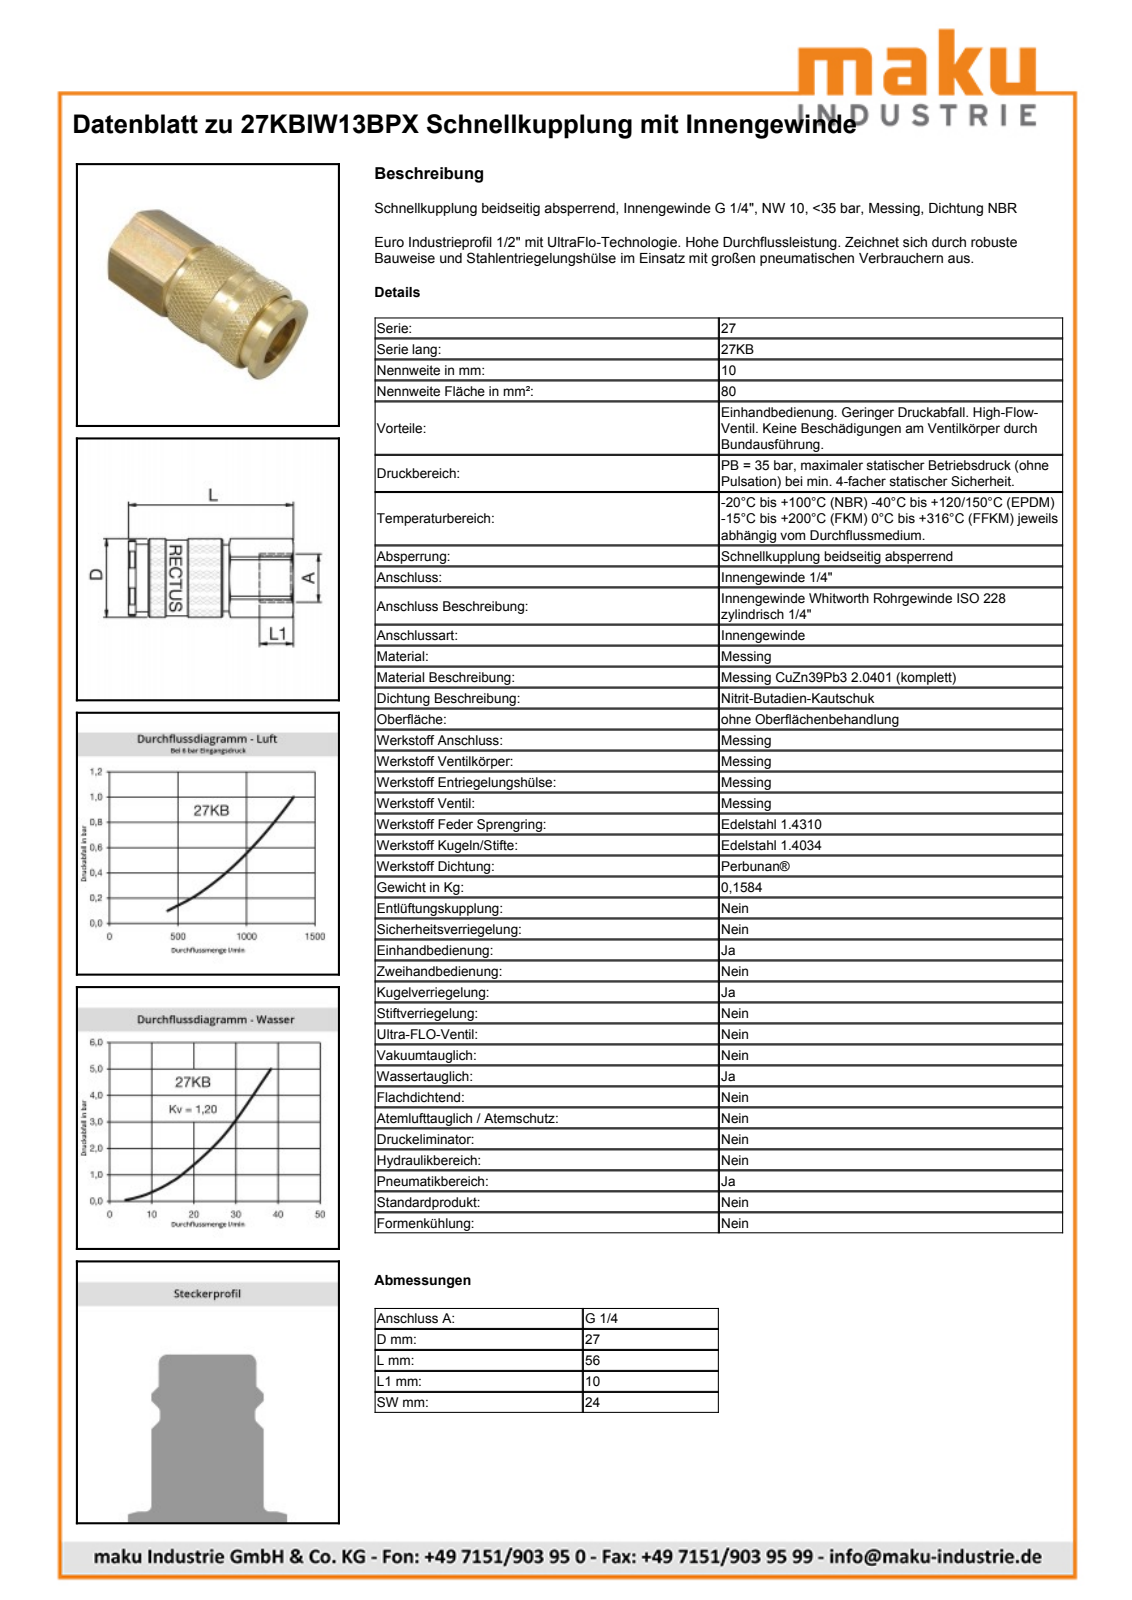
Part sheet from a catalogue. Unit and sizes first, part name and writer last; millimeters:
Units: millimetres
Overall size (bounding box): 56.45 × 27.15 × 27.15
Round holes (diameter × count): ⌀11.45 ×1, ⌀20.3 ×1, ⌀20.95 ×1, ⌀23.35 ×1, ⌀23.55 ×1
Round bosses / shafts (diameter × count): ⌀27.15 ×1, ⌀26 ×1, ⌀23.1 ×1, ⌀22.75 ×1, ⌀20 ×1
Partial cylindrical surfaces — rounded edges, fillets, slot ends (radius × count): R9.62 ×1, R12.9 ×1, R13.53 ×1
Main face-to-face distances: 24, 56.45, 31.75, 24.7, 48.12, 16.37, 8.33, 6.25, 25.5, 41.87
Volume: 26 442 mm³ · Surface area: 10 291 mm²
Bodies: 2 solids, 823 faces (320 planar, 87 cylindrical, 416 other)
Part name (STEP PRODUCT): D109087
STEP written by: Autodesk Inventor 2013 (AUTOMOTIVE_DESIGN)
